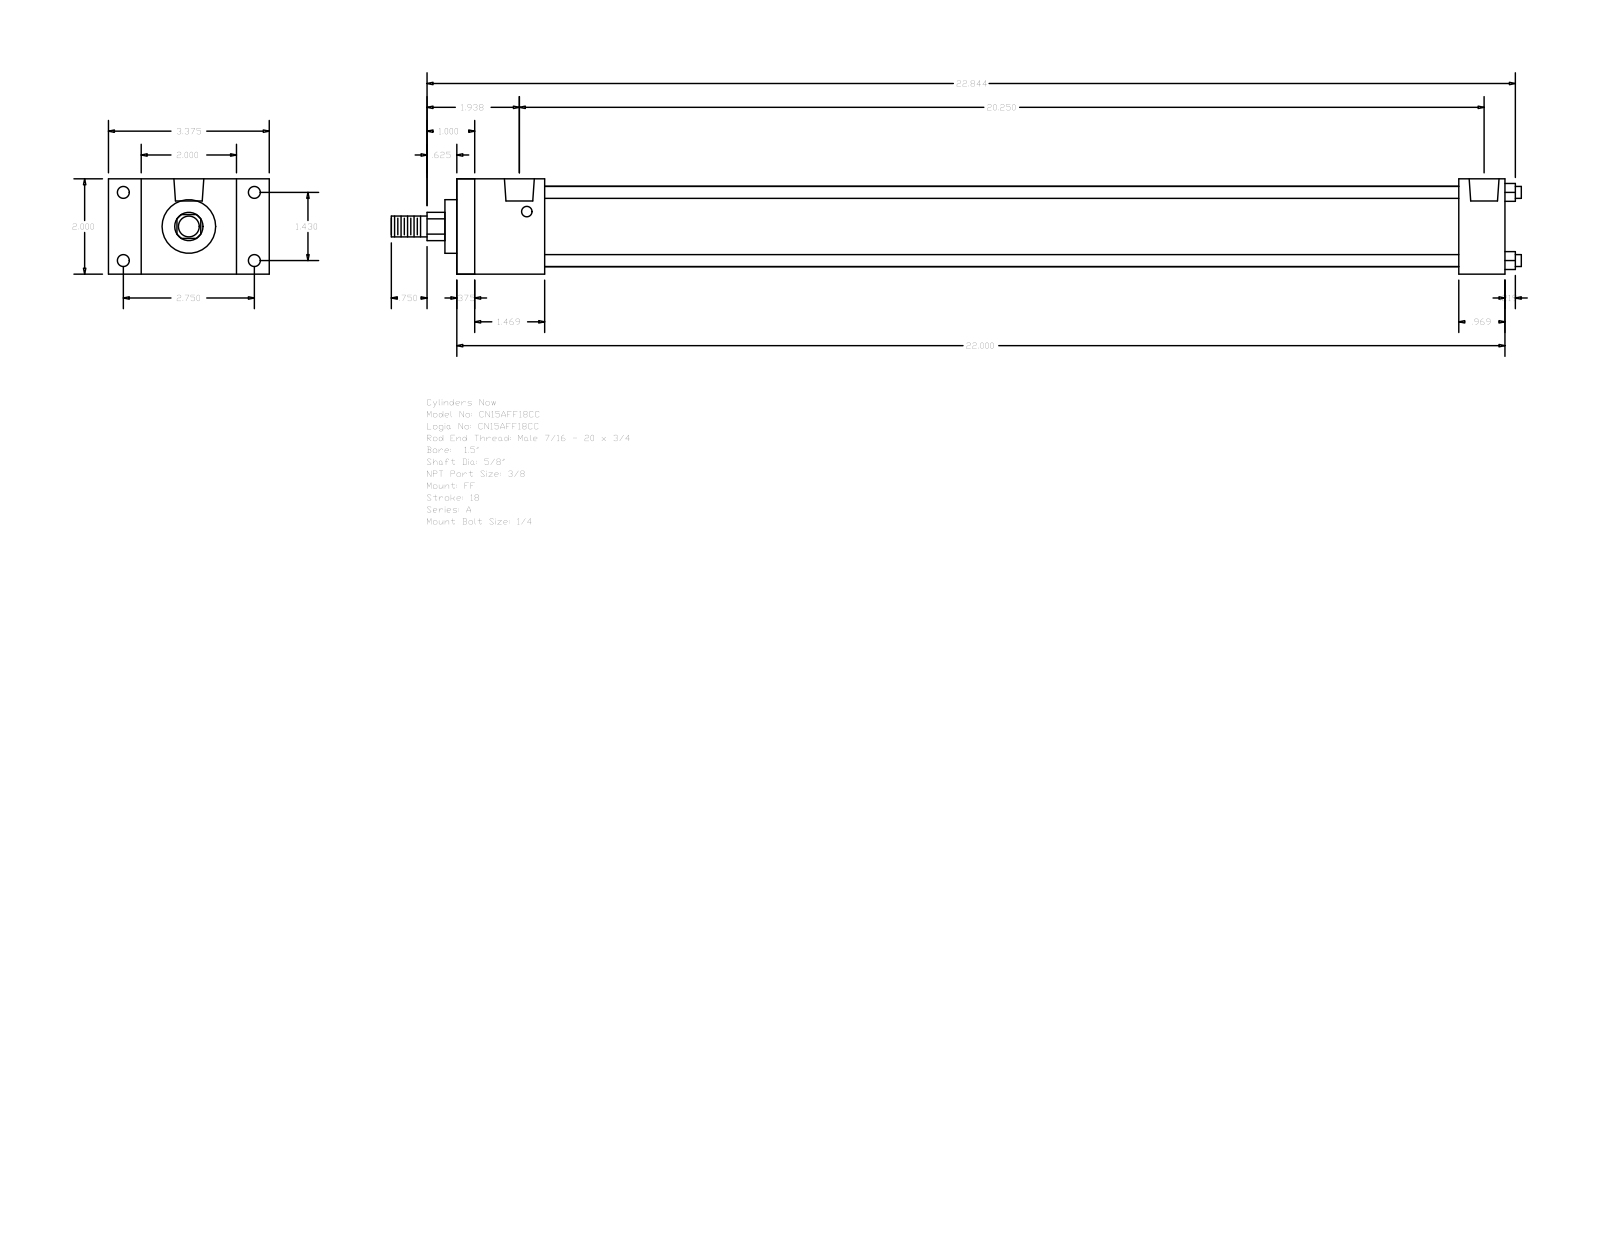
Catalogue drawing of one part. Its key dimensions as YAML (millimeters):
part_name: "A_FF__0150_0.625"
step_written_by: "GSSL Pune (CONFIG_CONTROL_DESIGN)"
units: millimeters
bodies: {solids: 0, faces: 92, planar: 64, cylindrical: 28, other: 0}
overall_size: [602.46, 85.72, 50.8]
round_holes:
  - {diameter: 5.56, count: 4}
  - {diameter: 6.35, count: 4}
  - {diameter: 15.93, count: 2}
round_bosses_or_shafts:
  - {diameter: 6.35, count: 4}
  - {diameter: 42.93, count: 1}
  - {diameter: 28.57, count: 1}
  - {diameter: 15.88, count: 1}
  - {diameter: 11.11, count: 1}
partial_cylinders:
  - {radius: 7.54, count: 1}
face_to_face_distances: [50.8, 558.79, 9.52, 549.27, 46.83, 534.19, 37.31, 524.67, 487.36, 511.96]
hole_center_spacings: [3.97, 36.32, 69.84, 78.72, 506.41, 510.38, 514.35]
